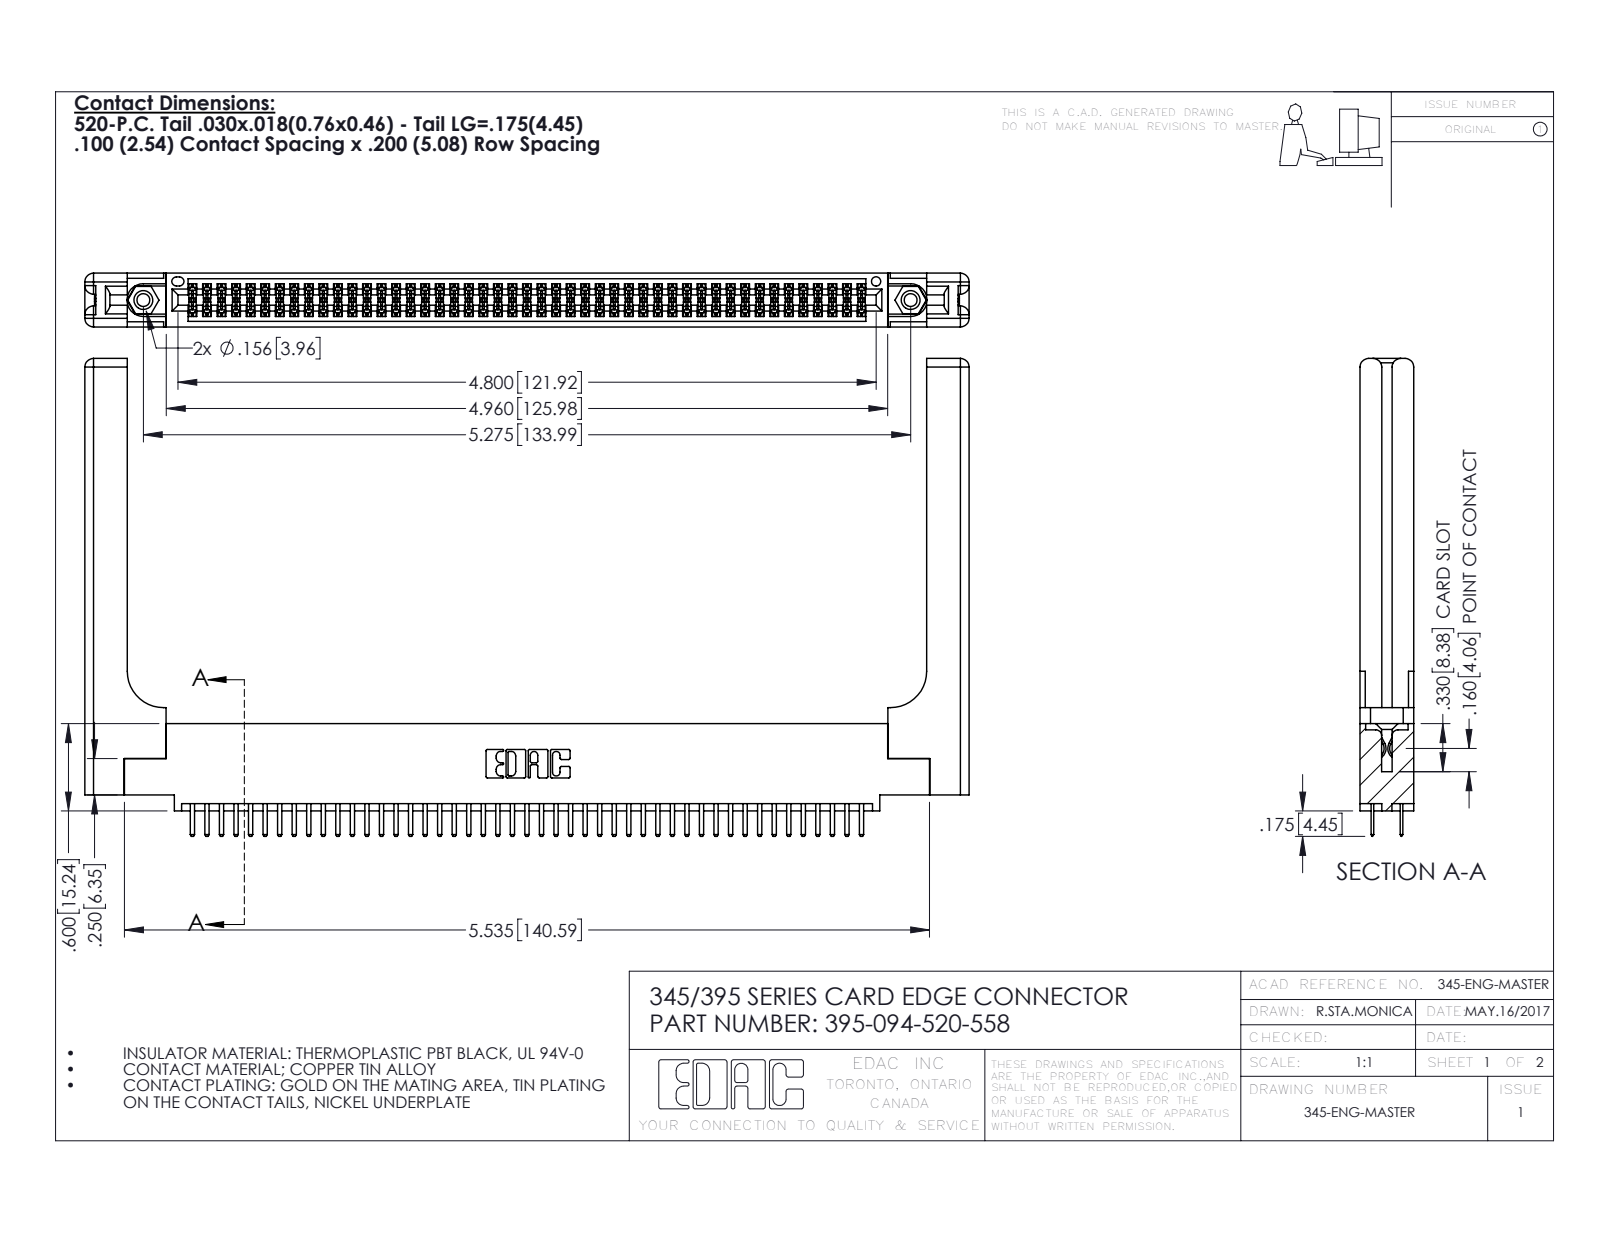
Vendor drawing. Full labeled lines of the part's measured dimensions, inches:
Part name (STEP PRODUCT): 345-250-001_345-250-001-102; 345 Part_0.110 Offset - 0.156 Dia-TH; 345-292-001_345-293-120; 395-094-520-558 (+1 more)
STEP written by: SolidWorks 2016 (CONFIG_CONTROL_DESIGN)
Units: inches
Bodies: 99 solids, 5462 faces (3522 planar, 1880 cylindrical, 60 other)
Overall size (bounding box): 6.079 × 3.285 × 0.37
Volume: 1.428 in³ · Surface area: 42.21 in²
Round holes (diameter × count): ⌀0.089 ×2, ⌀0.125 ×2, ⌀0.156 ×2, ⌀0.064 ×1
Round bosses / shafts (diameter × count): ⌀0.155 ×2
Partial cylindrical surfaces — rounded edges, fillets, slot ends (radius × count): R0.006 ×141, R0.01 ×98, R0.01 ×22, R0.06 ×16, R0.007 ×6, R0.031 ×6, R0.026 ×3, R0.014 ×2
Main face-to-face distances: 0.072, 0.37, 0.298, 0.2, 0.098, 0.272, 0.025, 0.225, 0.148, 0.15
Hole centre spacings: 0.27, 5.039, 5.275
